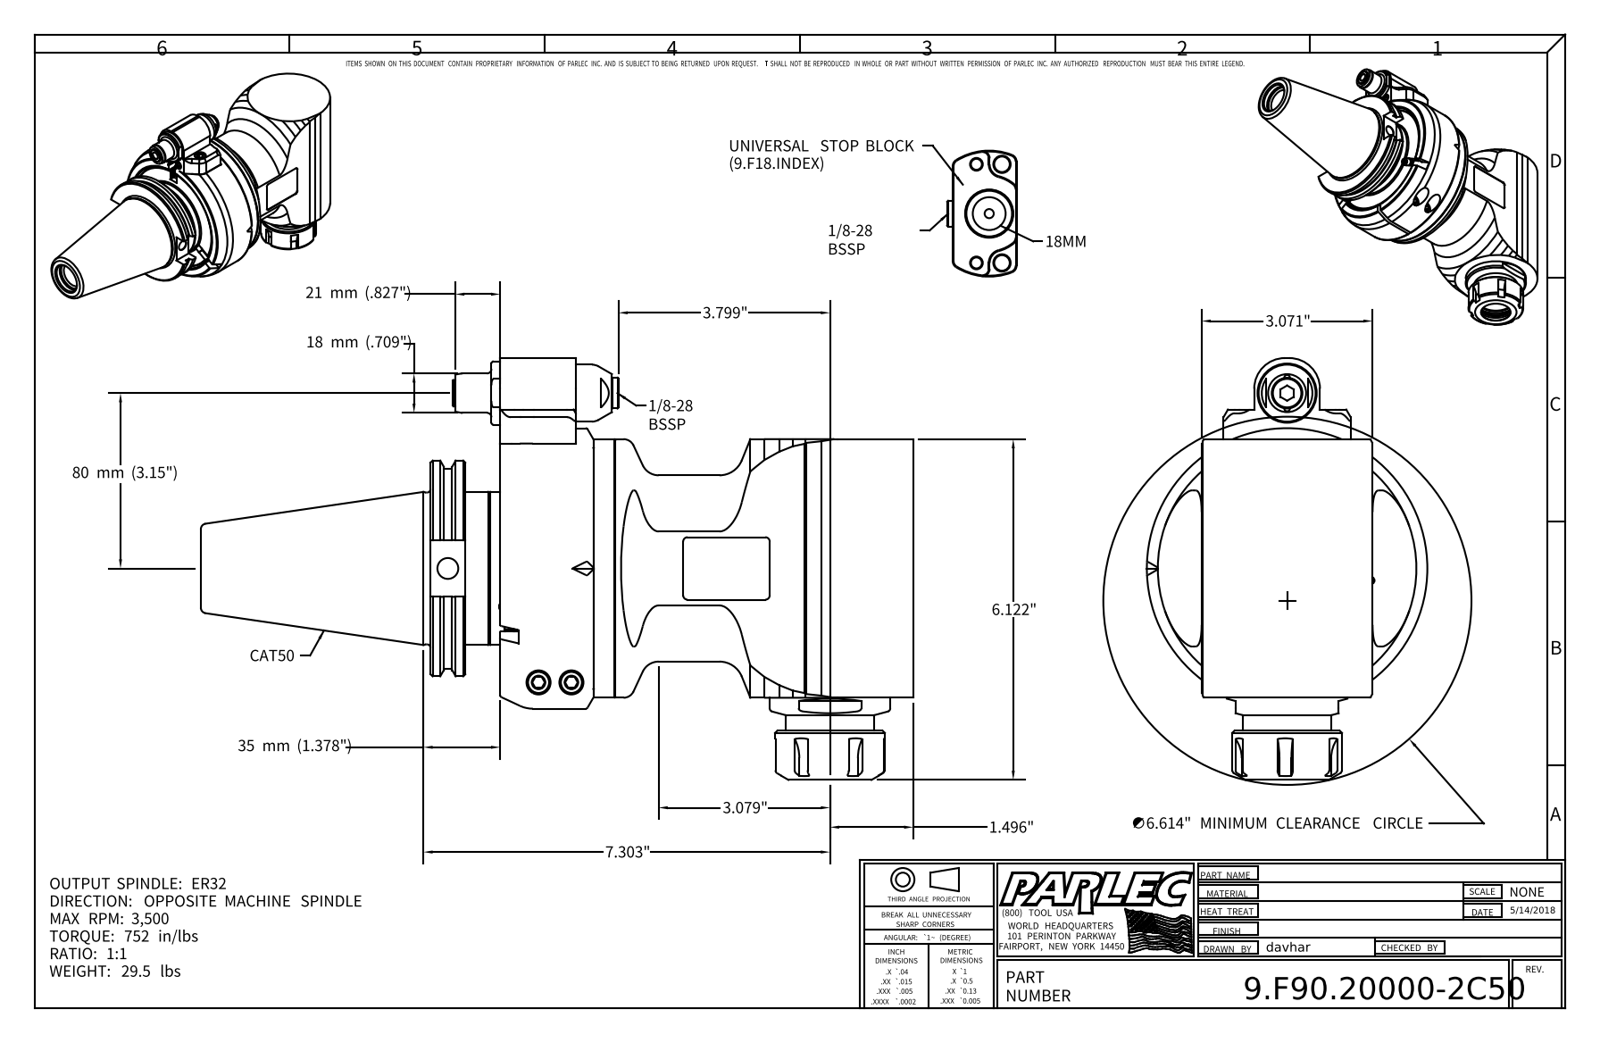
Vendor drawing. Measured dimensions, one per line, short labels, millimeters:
name: 9.F90.20000-2C50; 9.F90.20000; 9GA21C_458 (EVO, Type 2, Cat50, 80mm)
written by: Autodesk Inventor 2022 (AUTOMOTIVE_DESIGN)
unit: mm
bodies: 4 solids, 594 faces (267 planar, 153 cylindrical, 174 other)
size: 325.1 × 192.5 × 128
volume: 2 080 000 mm³; area: 215 900 mm²
holes: 3× ⌀5, 3× ⌀6.5, 3× ⌀12.5, 2× ⌀2.6, 2× ⌀3.3, 2× ⌀4.2, 2× ⌀8, 2× ⌀10.4, 2× ⌀11, 2× ⌀27, 1× ⌀2.5, 1× ⌀3
bosses: 4× ⌀10, 3× ⌀12, 2× ⌀18, 2× ⌀6, 2× ⌀2.5, 1× ⌀128, 1× ⌀118, 1× ⌀117.6
rounds: 14× R1, 12× R2, 6× R3, 6× R15, 4× R4, 2× R0.5, 2× R3.5, 2× R8
face distances: 0.5, 1, 6.5, 35, 40.5, 2, 35.5, 5.5, 8.5, 5
hole spacings: 7, 12.8, 18.8, 25.3, 63.5, 14, 15, 16
